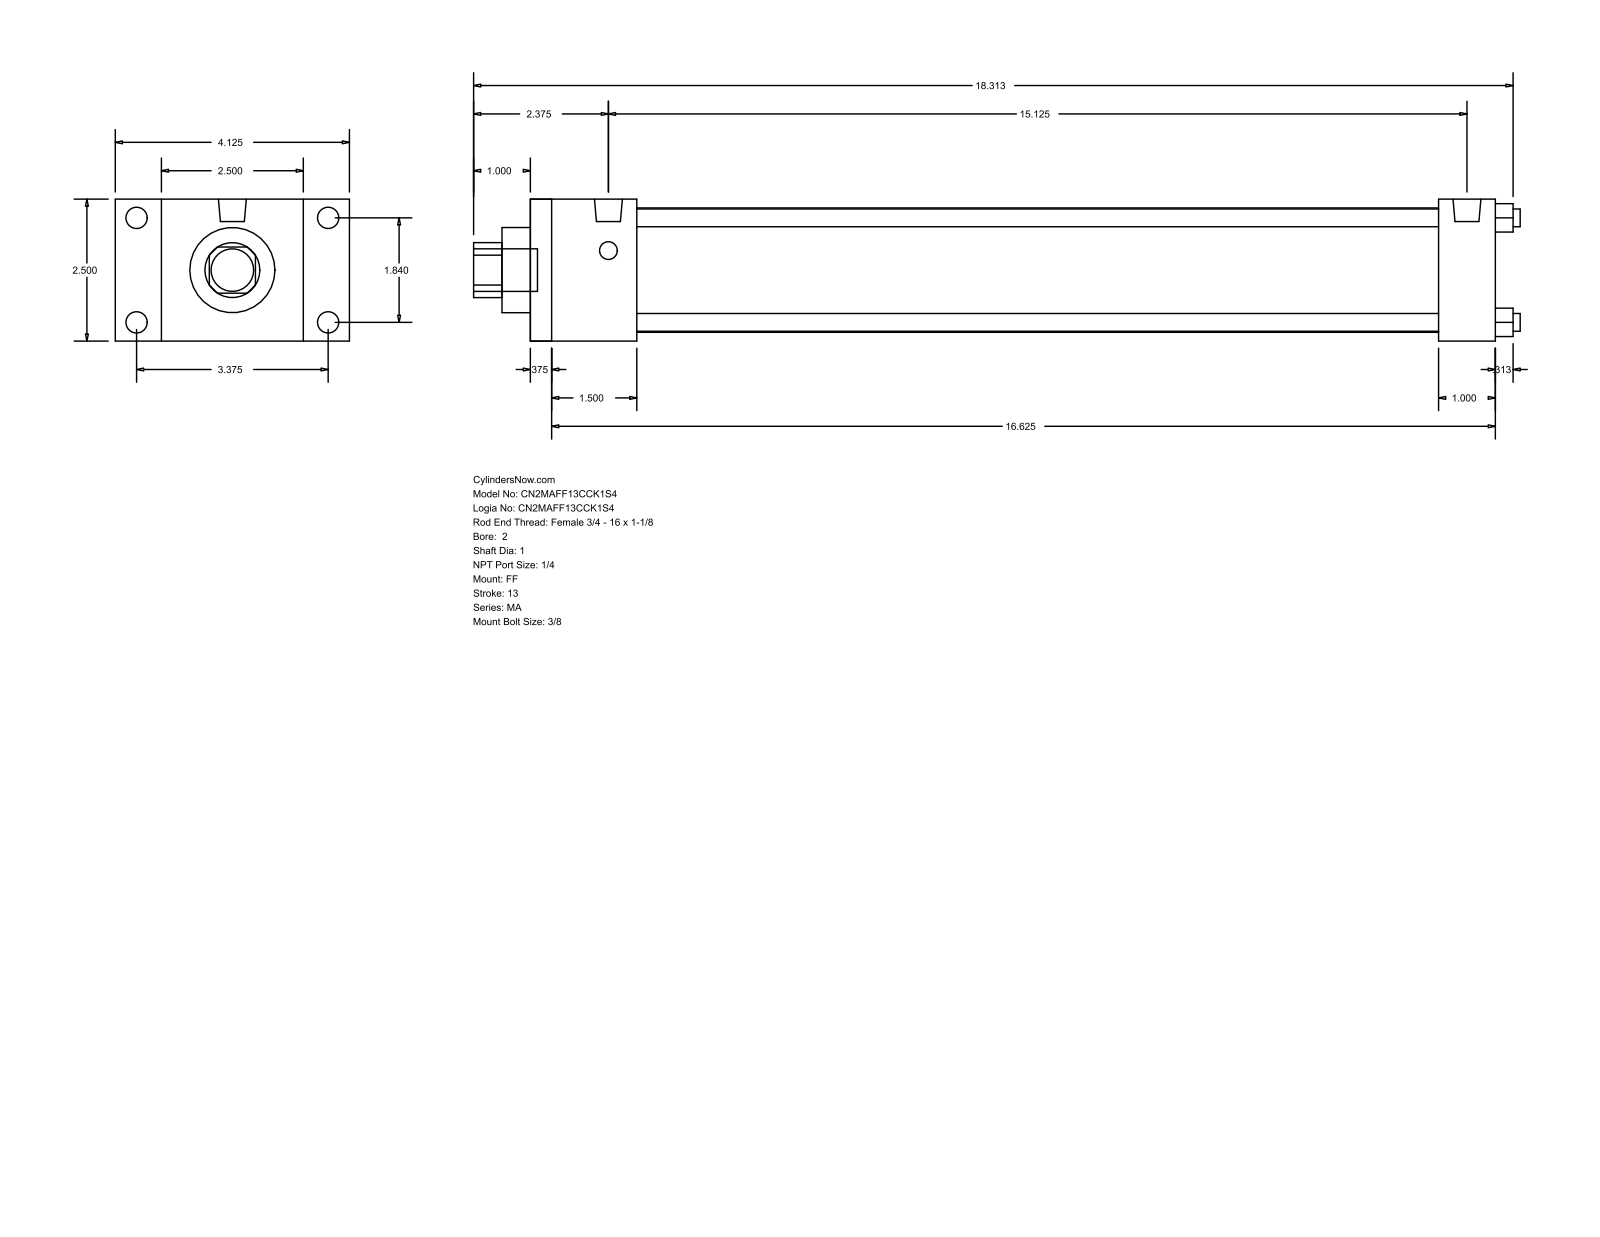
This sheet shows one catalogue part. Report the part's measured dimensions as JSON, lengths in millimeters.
{"part_name": "MA_FF__0200_1", "step_written_by": "GSSL Pune (CONFIG_CONTROL_DESIGN)", "units": "millimeters", "bodies": {"solids": 0, "faces": 92, "planar": 64, "cylindrical": 28, "other": 0}, "overall_size": [468.31, 104.78, 63.5], "round_holes": [[7.94, 4], [25.4, 1], [38.1, 1], [55.63, 1]], "round_bosses_or_shafts": [[9.53, 4], [7.94, 4], [12.49, 2], [19.05, 1]], "partial_cylinders_radius": [[12.29, 1]], "face_to_face_distances": [63.5, 431.8, 9.52, 422.28, 25.4, 20.64, 12.7, 47.63, 406.4, 38.11], "hole_center_spacings": [33.05, 46.74, 66.1]}
